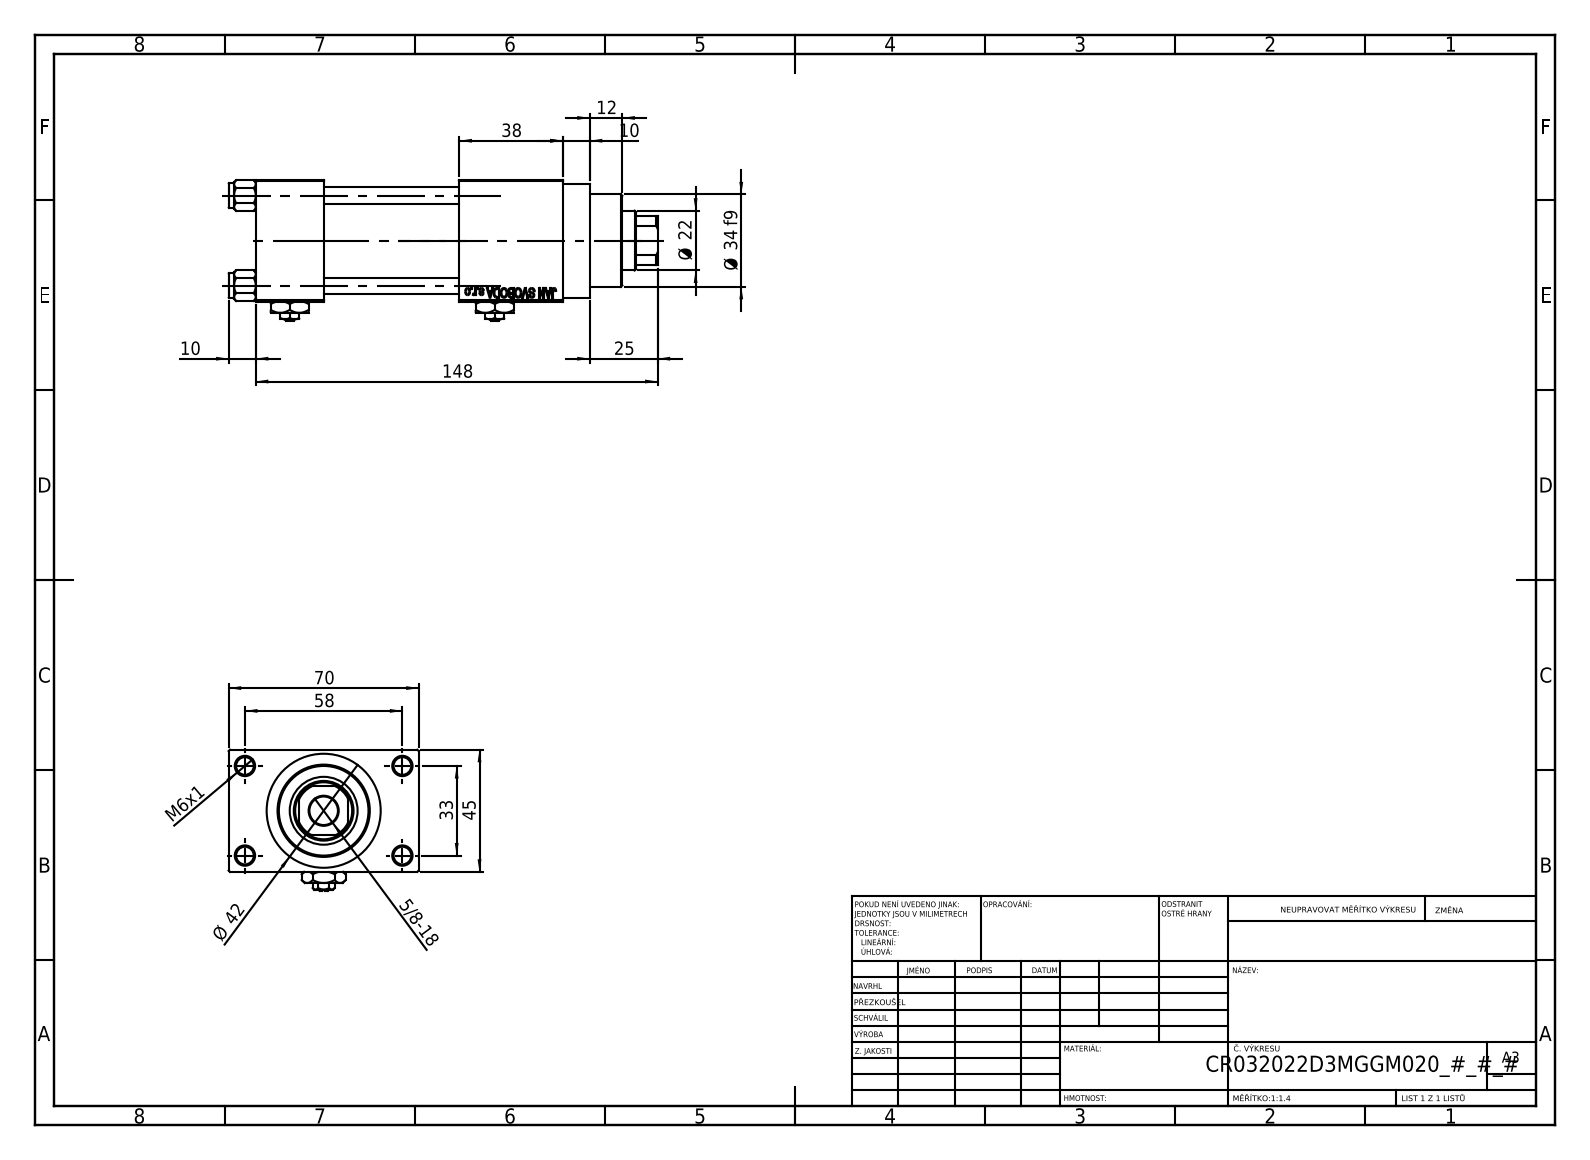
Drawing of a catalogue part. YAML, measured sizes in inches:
part_name: "V215CR_D_Body; V215CR_D_TYCINKA; V215CR_VCP_D; Zatka_pro_OIL_PORT (+2 more)"
step_written_by: "SolidWorks 2019 (CONFIG_CONTROL_DESIGN)"
units: inches
bodies: {solids: 13, faces: 1202, planar: 542, cylindrical: 100, other: 560}
overall_size: [6.22, 2.756, 2.047]
volume: 14.85
surface_area: 125.9
round_holes:
  - {diameter: 0.236, count: 4}
  - {diameter: 0.256, count: 4}
  - {diameter: 0.276, count: 2}
  - {diameter: 0.518, count: 2}
  - {diameter: 0.787, count: 2}
  - {diameter: 0.413, count: 1}
  - {diameter: 0.866, count: 1}
  - {diameter: 0.945, count: 1}
  - {diameter: 0.984, count: 1}
  - {diameter: 1.26, count: 1}
  - {diameter: 1.299, count: 1}
round_bosses_or_shafts:
  - {diameter: 0.354, count: 4}
  - {diameter: 1.654, count: 1}
  - {diameter: 1.496, count: 1}
  - {diameter: 1.339, count: 1}
partial_cylinders:
  - {radius: 0.413, count: 1}
face_to_face_distances: [1.772, 0.984, 0.492, 2.264, 1.969, 2.953, 3.465, 2.756, 1.496, 4.449]
hole_center_spacings: [0.488, 0.924, 1.307, 1.314, 1.392, 1.795, 2.219, 1.299]
